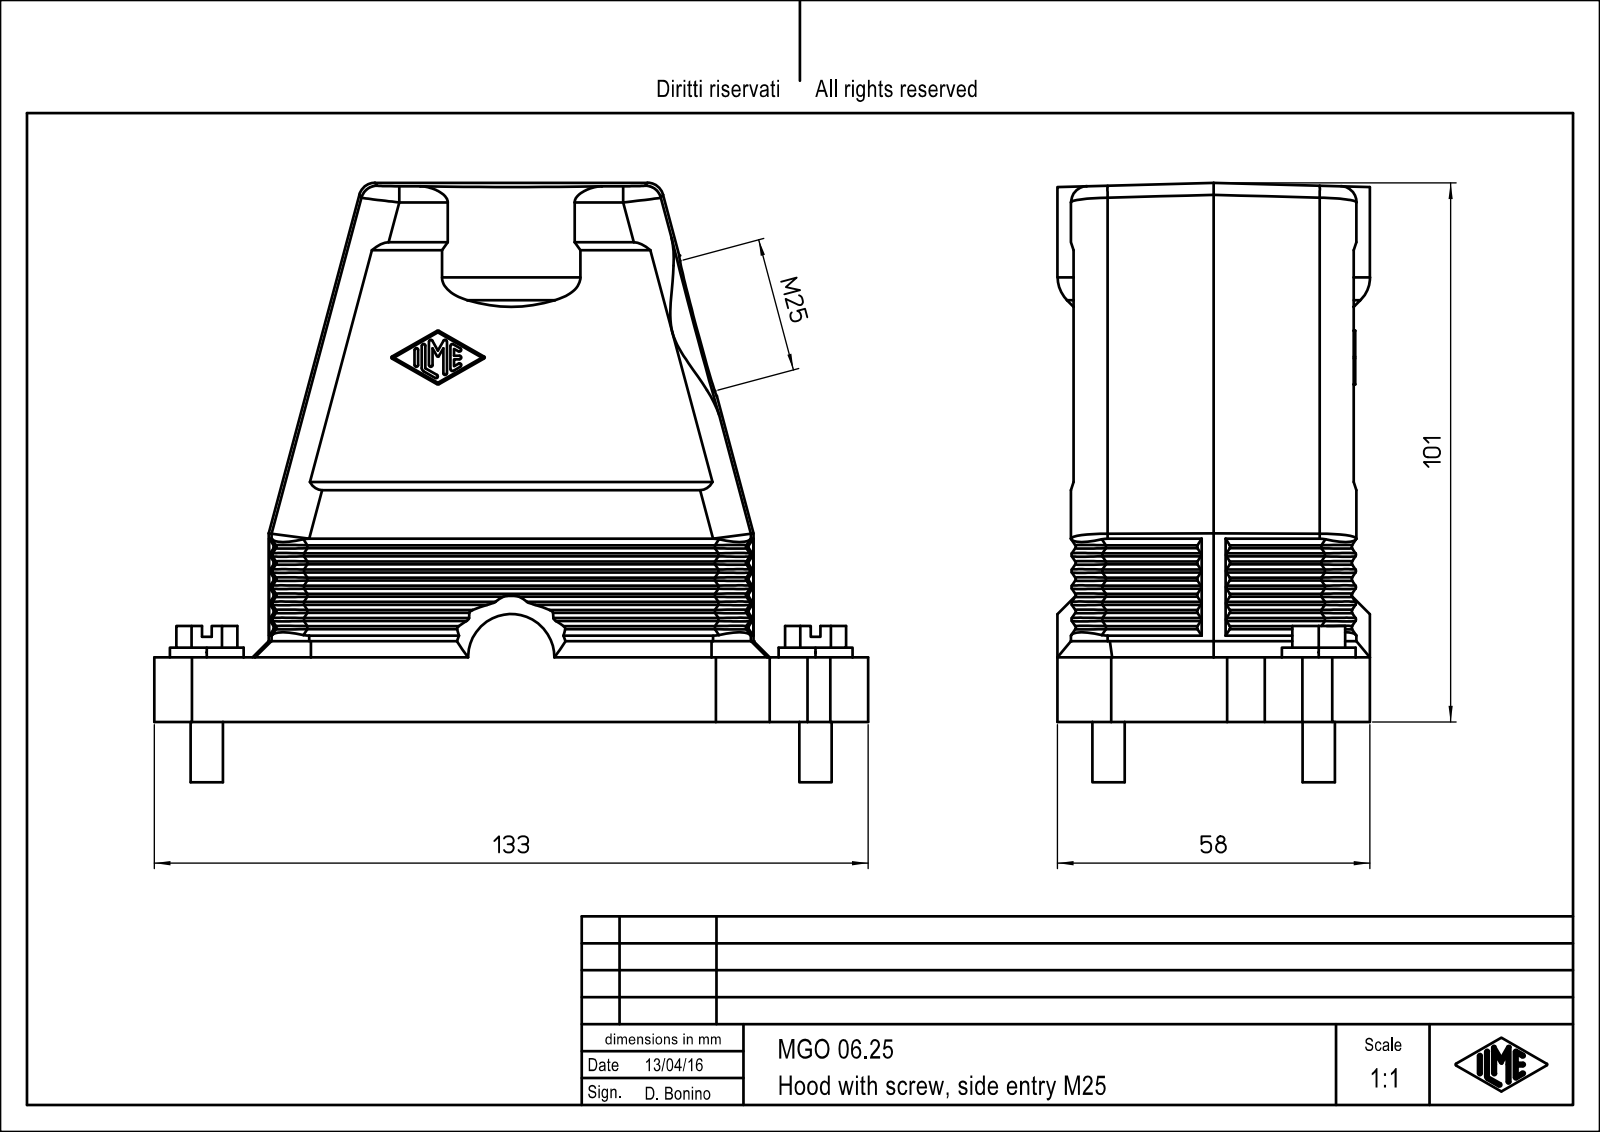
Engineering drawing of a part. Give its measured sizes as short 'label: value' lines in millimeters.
name: MGO_06.25
written by: PTC Creo Elements/Direct Modeling 19.0B 21-Mar-2015 (C) Parametric Technology GmbH (AUTOMOTIVE_DESIGN)
unit: mm
bodies: 1 solid, 511 faces (245 planar, 124 cylindrical, 142 other)
size: 132.5 × 111.2 × 58
volume: 146 584 mm³; area: 63 564 mm²
holes: 4× ⌀3, 1× ⌀25
bosses: 2× ⌀13.7, 2× ⌀6
rounds: 62× R7, 15× R0.33, 4× R3, 4× R5.5, 4× R8.5, 3× R0.17, 2× R10, 1× R0.67
face distances: 3, 55, 52, 2.5, 6, 44.5, 3.33, 0.5, 55.5, 52.5
hole spacings: 27, 44, 51.62
